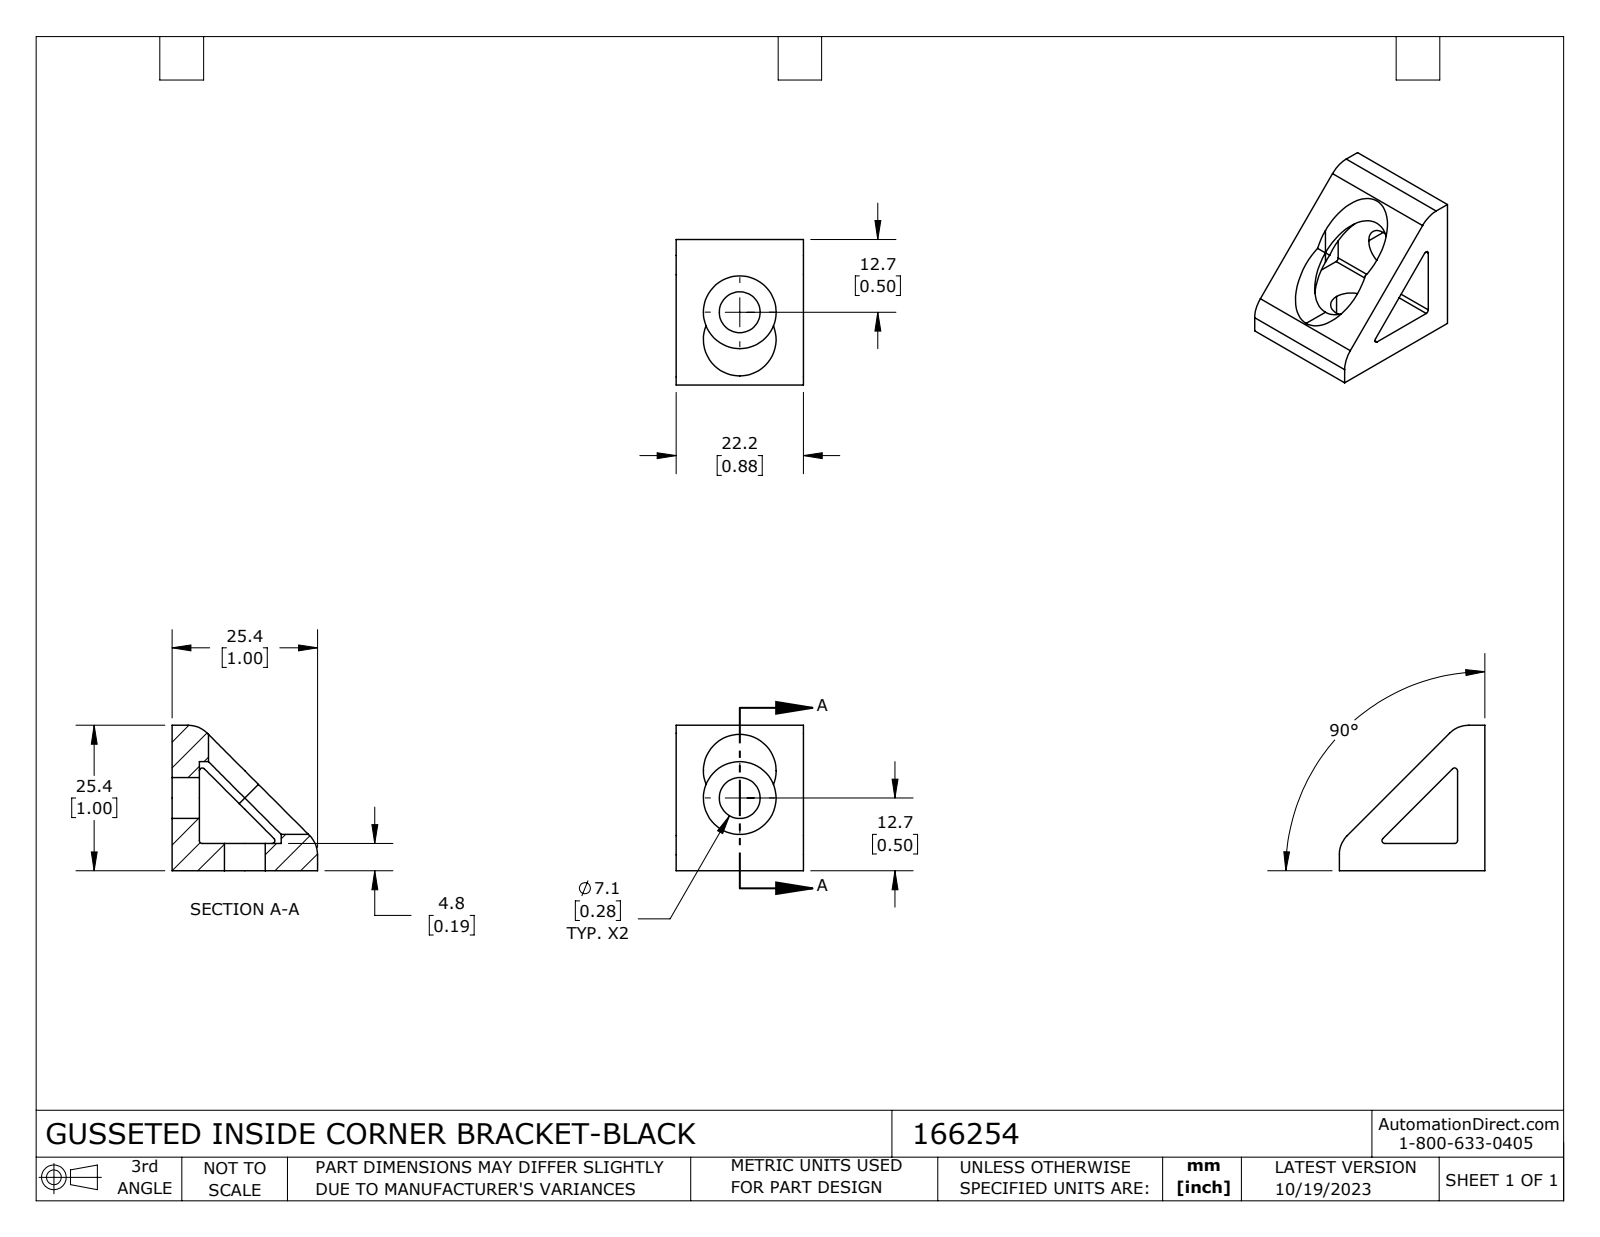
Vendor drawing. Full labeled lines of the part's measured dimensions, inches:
Part name (STEP PRODUCT): 166254
STEP written by: SolidWorks 2023 (CONFIG_CONTROL_DESIGN)
Units: inches
Bodies: 1 solid, 31 faces (11 planar, 20 cylindrical, 0 other)
Overall size (bounding box): 1 × 1 × 0.875
Volume: 0.369 in³ · Surface area: 5.481 in²
Round holes (diameter × count): ⌀0.281 ×2, ⌀0.5 ×2
Partial cylindrical surfaces — rounded edges, fillets, slot ends (radius × count): R0.02 ×3, R0.187 ×1, R0.188 ×1
Main face-to-face distances: 0.187, 0.875, 1, 0.813
